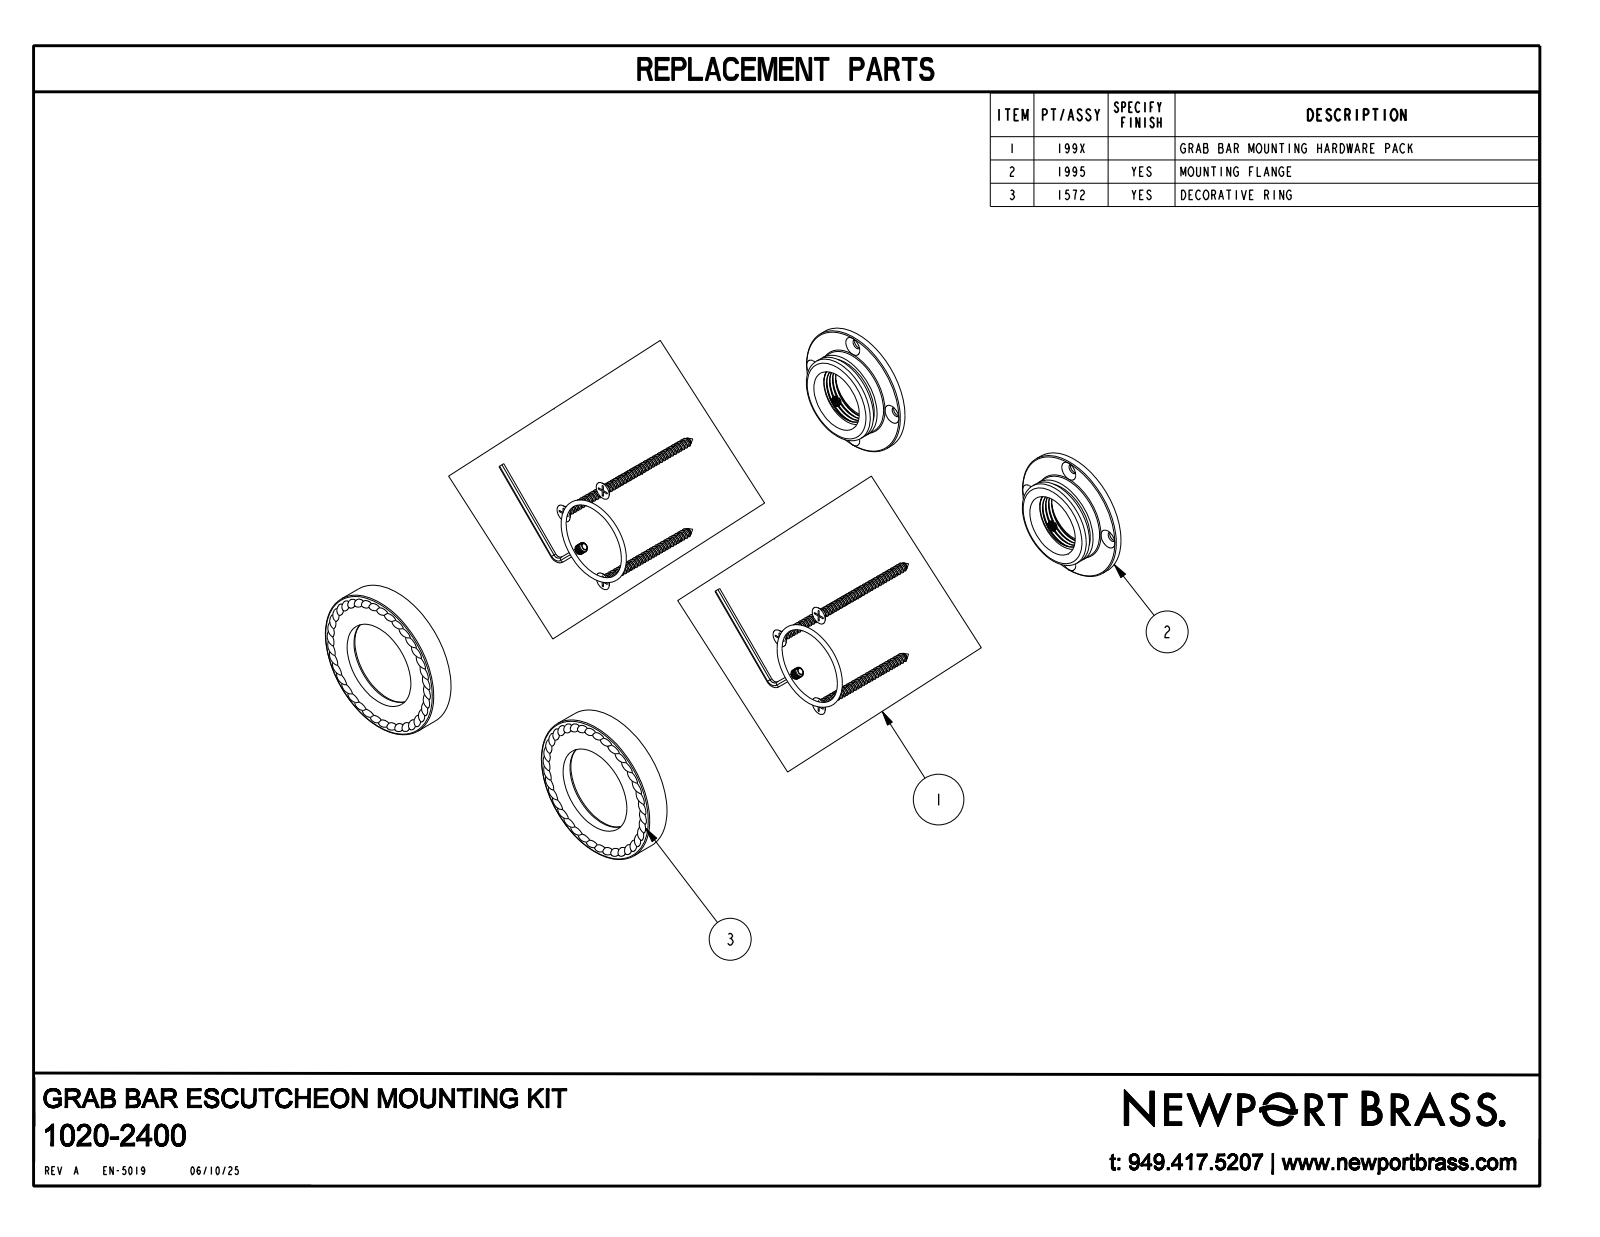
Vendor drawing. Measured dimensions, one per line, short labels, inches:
name: 1995; 1572; 1020-2400_ASM
written by: CREO PARAMETRIC BY PTC INC, 2019352 (CONFIG_CONTROL_DESIGN)
unit: in
bodies: 4 solids, 470 faces (36 planar, 132 cylindrical, 302 other)
size: 9 × 3 × 0.6
volume: 3.723 in³; area: 101.1 in²
holes: 8× ⌀0.202, 2× ⌀0.163, 2× ⌀1.16, 2× ⌀1.26, 2× ⌀1.77, 2× ⌀2.842
bosses: 2× ⌀3, 2× ⌀2.6, 2× ⌀1.93, 2× ⌀1.75, 2× ⌀1.594, 2× ⌀0.197
rounds: 8× R0.212
face distances: 0.5, 0.42, 0.08, 0.15, 0.35, 0.1, 0.27, 0.45, 0.6, 0.18
hole spacings: 1.087, 1.538, 6, 2.175, 5.031, 6.098, 7.17, 4.913
